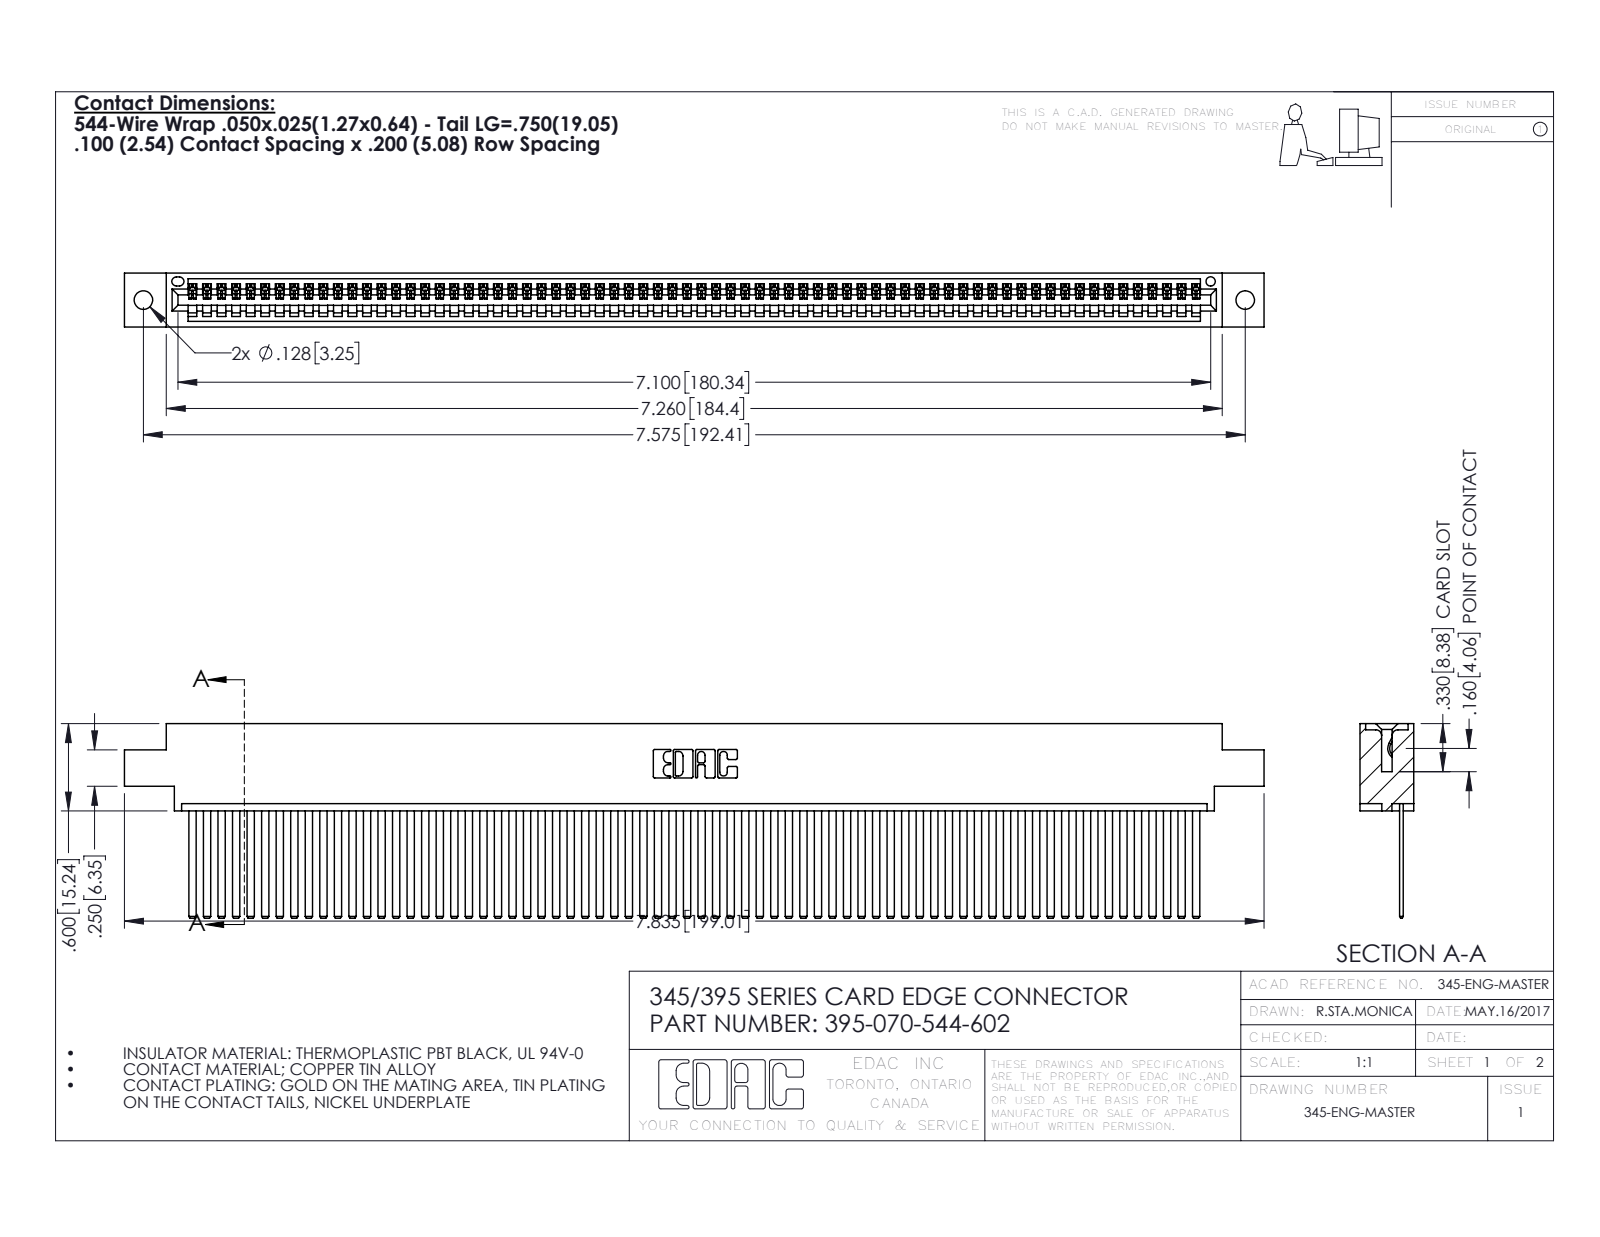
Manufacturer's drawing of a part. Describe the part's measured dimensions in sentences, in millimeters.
The part is named "345-292-001_345-293-144; 395-070-544-602; 345 Part_0.170 Offset - 0.128 Dia". Its 3-D file was written by "SolidWorks 2016 (CONFIG_CONTROL_DESIGN)". It is 71 solids with 3770 faces: 2604 planar, 1166 cylindrical and 0 other. Overall it measures 199 by 34 by 9.4 millimeters. Its volume is 19 800 cubic millimeters and its surface area 28 970 square millimeters. Round holes: 2 of diameter 3.3, 1 of diameter 1.6. Partial cylindrical surfaces (rounded edges, fillets, slot ends): 140 of radius 0.2, 22 of radius 0.3, 6 of radius 0.2, 6 of radius 0.8, 3 of radius 0.7, 2 of radius 0.8, 2 of radius 1, 1 of radius 0.4. The main face-to-face distances are 1.8, 7.6, 0.6, 2.5, 6.9, 9.4, 5.1, 5.7, 4.4, 3.8. The hole center spacings are 6.9, 186.4, 192.4.
